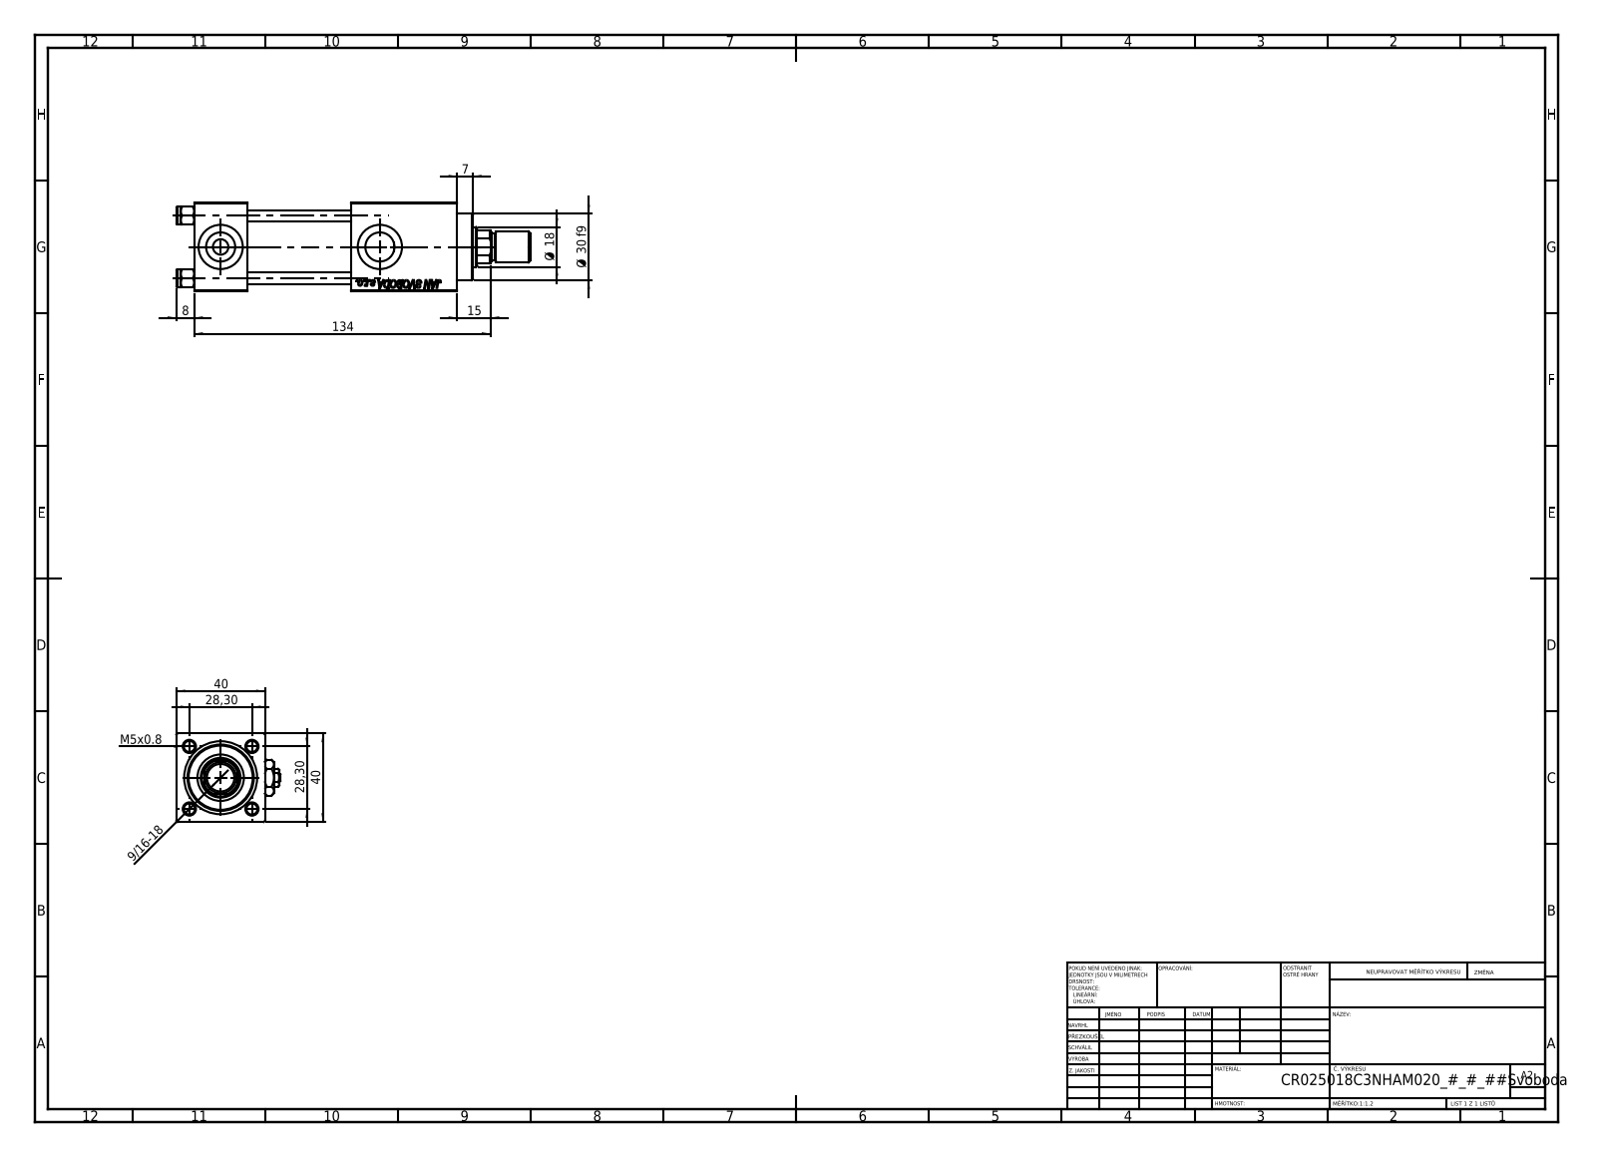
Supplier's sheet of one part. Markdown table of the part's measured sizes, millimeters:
| quantity | value |
| --- | --- |
| part name | V215_VC_A; V215CR_C_Body; ROD_END_AH; NUT_M5_C (+3 more) |
| STEP written by | SolidWorks 2019 (CONFIG_CONTROL_DESIGN) |
| units | millimeters |
| bodies | 14 solids, 1259 faces (575 planar, 100 cylindrical, 584 other) |
| overall size | 160 × 47 × 40 |
| volume | 151 265 mm³ |
| surface area | 59 611 mm² |
| round holes (diameter × count) | 5 × 4, 20 × 3, 7 × 2, 13.16 × 2, 8.5 × 1, 18 × 1, 21 × 1, 25 × 1, 30 × 1 |
| round bosses / shafts (diameter × count) | 8 × 4, 31 × 1, 14 × 1, 12 × 1 |
| partial cylindrical surfaces (radius × count) | 8.5 × 1 |
| main face-to-face distances | 40, 24, 39.8, 47, 71, 90.3, 66.3, 19.3, 48, 8 |
| hole center spacings | 20.01, 28.3, 40.02, 72 |
